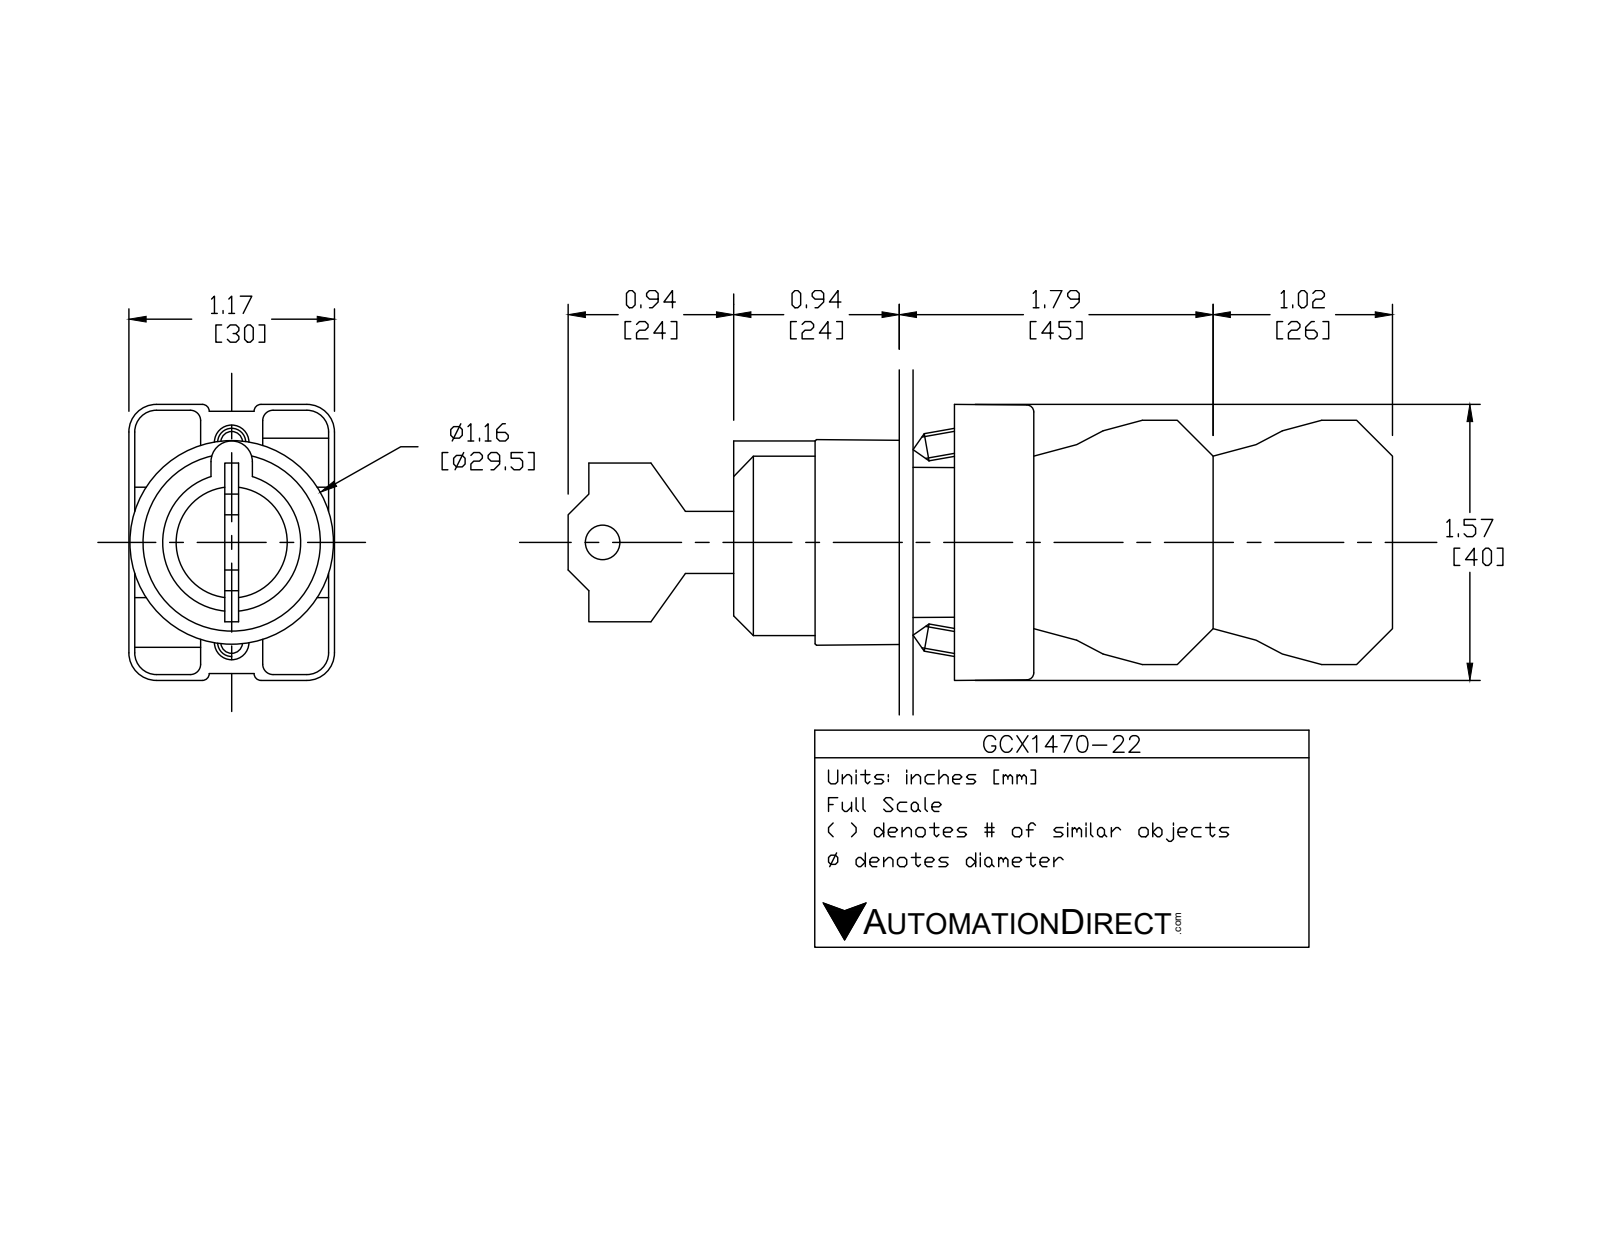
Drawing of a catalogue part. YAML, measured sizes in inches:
part_name: "ecx1030; GCX1470-22; ecx1040; ecx1029 (+1 more)"
step_written_by: "SolidWorks 2016 (AUTOMOTIVE_DESIGN)"
units: inches
bodies: {solids: 10, faces: 684, planar: 460, cylindrical: 184, other: 40}
overall_size: [3.675, 1.581, 1.177]
volume: 3.958
surface_area: 52.51
round_holes:
  - {diameter: 0.079, count: 4}
  - {diameter: 0.087, count: 2}
  - {diameter: 0.124, count: 2}
  - {diameter: 0.13, count: 2}
  - {diameter: 0.197, count: 1}
  - {diameter: 0.591, count: 1}
  - {diameter: 0.878, count: 1}
  - {diameter: 0.888, count: 1}
  - {diameter: 1.024, count: 1}
round_bosses_or_shafts:
  - {diameter: 0.157, count: 2}
  - {diameter: 1.175, count: 1}
  - {diameter: 1.004, count: 1}
  - {diameter: 0.965, count: 1}
  - {diameter: 0.945, count: 1}
  - {diameter: 0.856, count: 1}
  - {diameter: 0.78, count: 1}
  - {diameter: 0.571, count: 1}
partial_cylinders:
  - {radius: 0.059, count: 24}
  - {radius: 0.041, count: 12}
  - {radius: 0.124, count: 12}
  - {radius: 0.157, count: 12}
  - {radius: 0.039, count: 6}
  - {radius: 0.02, count: 2}
  - {radius: 0.063, count: 2}
  - {radius: 0.079, count: 2}
face_to_face_distances: [0.598, 0.579, 1.024, 0.02, 1.177, 1.744, 0.72, 0.031, 0.033, 0.309]
hole_center_spacings: [0.236, 0.544, 1.008, 0.98, 0.472, 0.49, 1.088]
